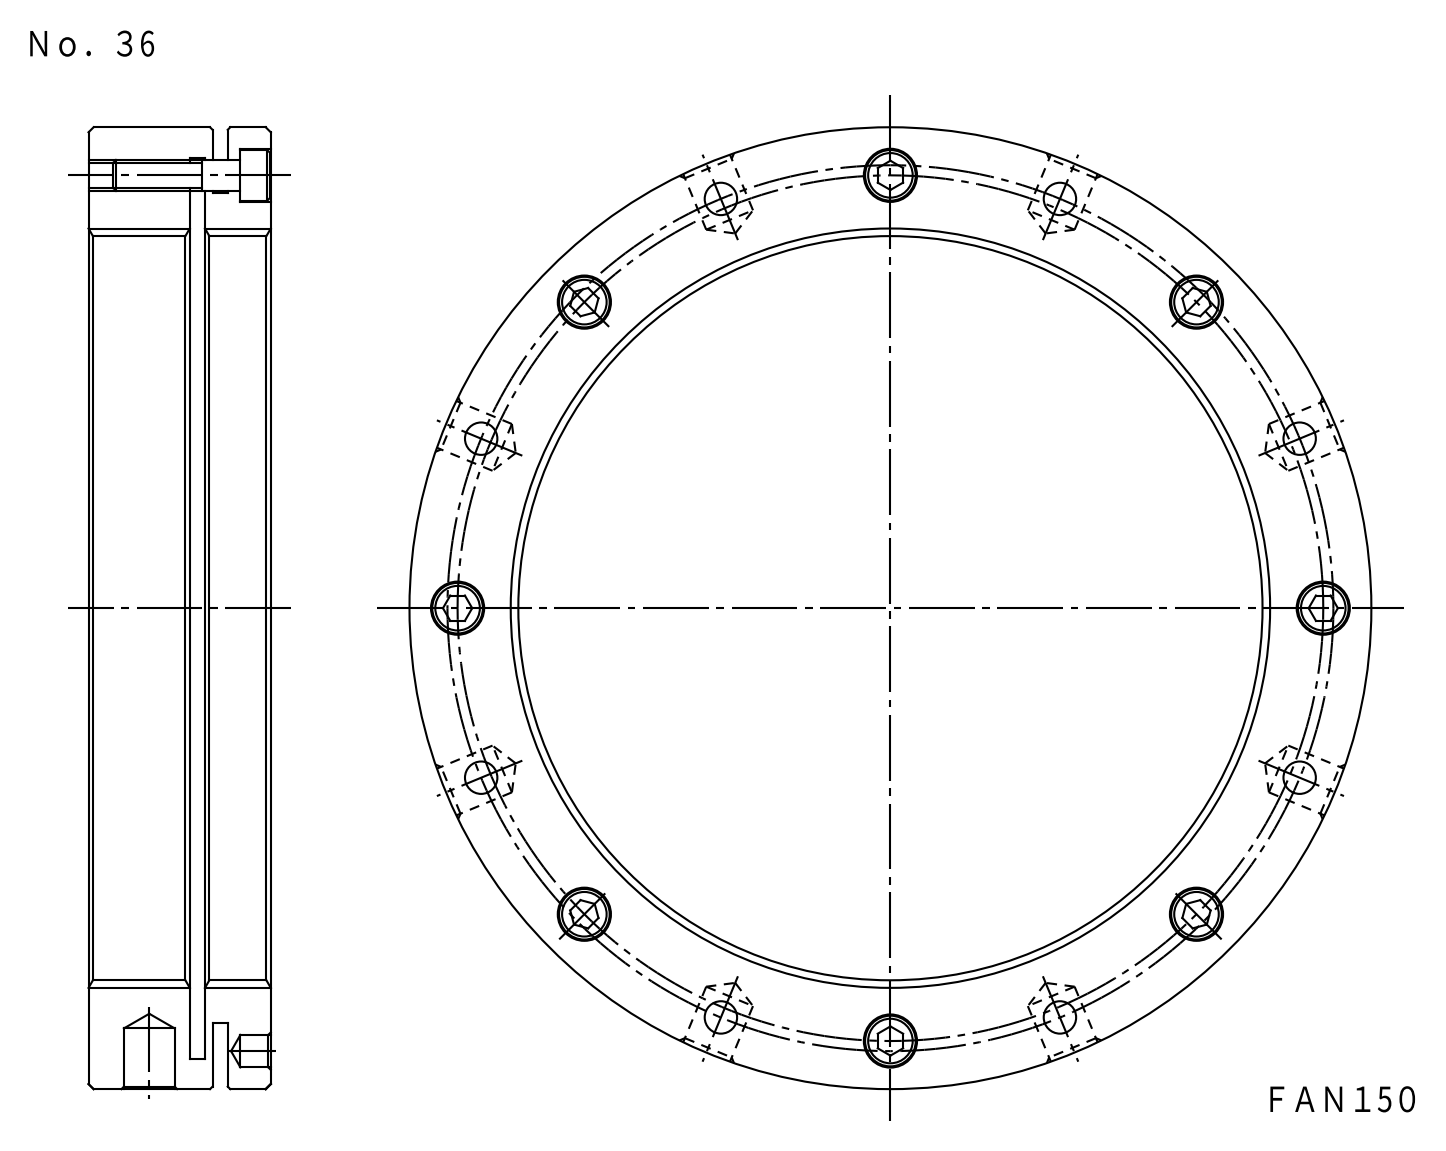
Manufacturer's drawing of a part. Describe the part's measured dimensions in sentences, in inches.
The part is named "FKD FAN150; M6X25_default". Its 3-D file was written by "SolidWorks 2012 (CONFIG_CONTROL_DESIGN)". It is 9 solids with 266 faces: 94 planar, 140 cylindrical and 32 other. Overall it measures 7.48 by 7.48 by 1.417 inches. Its volume is 20.23 cubic inches and its surface area 159.9 square inches. Round holes: 8 of diameter 0.252, 8 of diameter 0.268, 8 of diameter 0.394, 8 of diameter 0.433, 6 of diameter 0.194, 2 of diameter 0.194, 1 of diameter 5.906, 1 of diameter 7.008. Round bosses or shafts: 8 of diameter 0.394, 8 of diameter 0.236, 1 of diameter 7.48, 1 of diameter 6.457. The main face-to-face distances are 0.118, 0.177, 1.417, 0.787, 0.63, 0.965, 0.453, 1.083, 0.295, 0.335. The hole center spacings are 3.785, 6.68, 1.331, 1.331, 2.576, 3.366, 3.445, 4.761.
